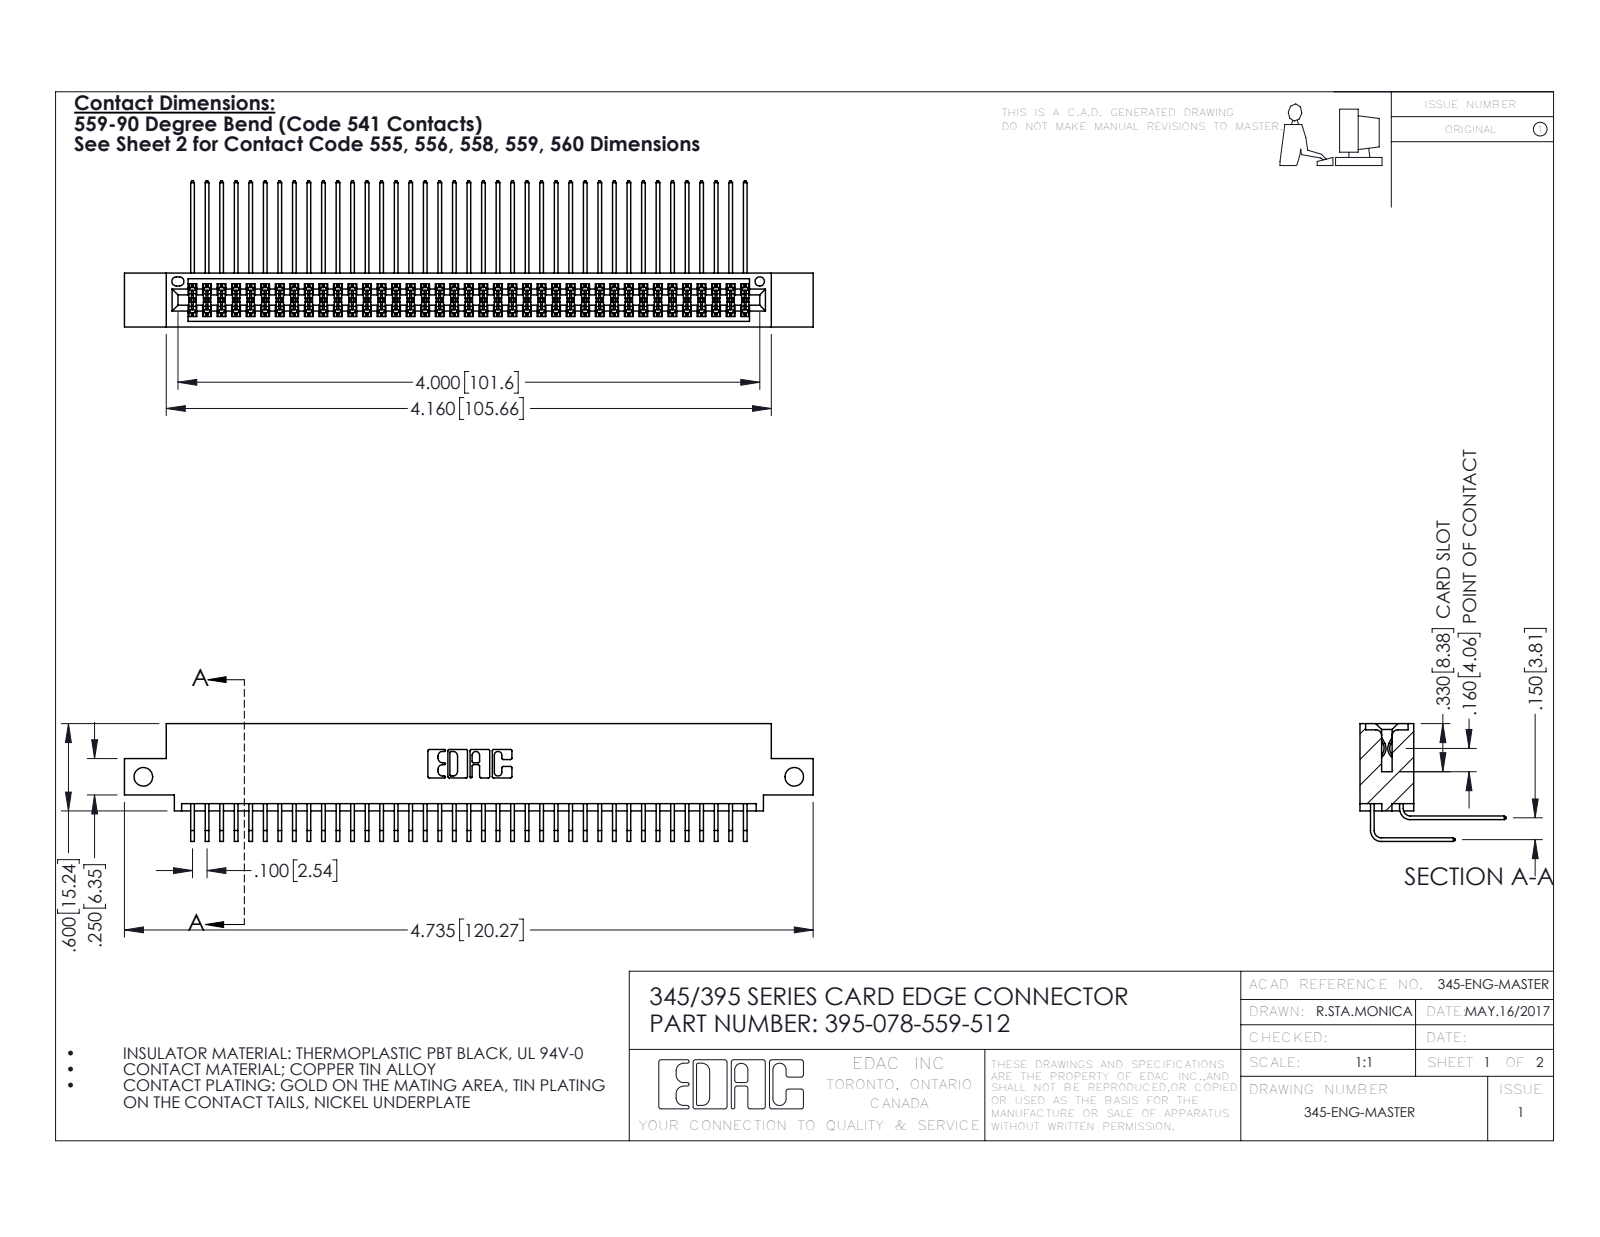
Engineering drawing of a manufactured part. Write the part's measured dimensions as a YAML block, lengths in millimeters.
part_name: "345-292-001_559 Tail - 2; 395-078-559-512; 345-292-001_558 559 Tail - 1; 345 Part_0.110 Offset - Side Mount"
step_written_by: "SolidWorks 2016 (CONFIG_CONTROL_DESIGN)"
units: millimeters
bodies: {solids: 79, faces: 4186, planar: 2814, cylindrical: 1372, other: 0}
overall_size: [120.3, 25.5, 20.5]
volume: 11900
surface_area: 19670
round_holes:
  - {diameter: 3.3, count: 2}
  - {diameter: 1.6, count: 1}
partial_cylinders:
  - {radius: 0.2, count: 117}
  - {radius: 0.3, count: 22}
  - {radius: 0.2, count: 6}
  - {radius: 0.8, count: 6}
  - {radius: 0.7, count: 3}
  - {radius: 0.4, count: 2}
  - {radius: 0.5, count: 2}
  - {radius: 0.6, count: 2}
face_to_face_distances: [1.8, 7.6, 5.1, 9.4, 2.5, 6.9, 0.6, 5.7, 4.4, 3.8]
hole_center_spacings: [113.7]
